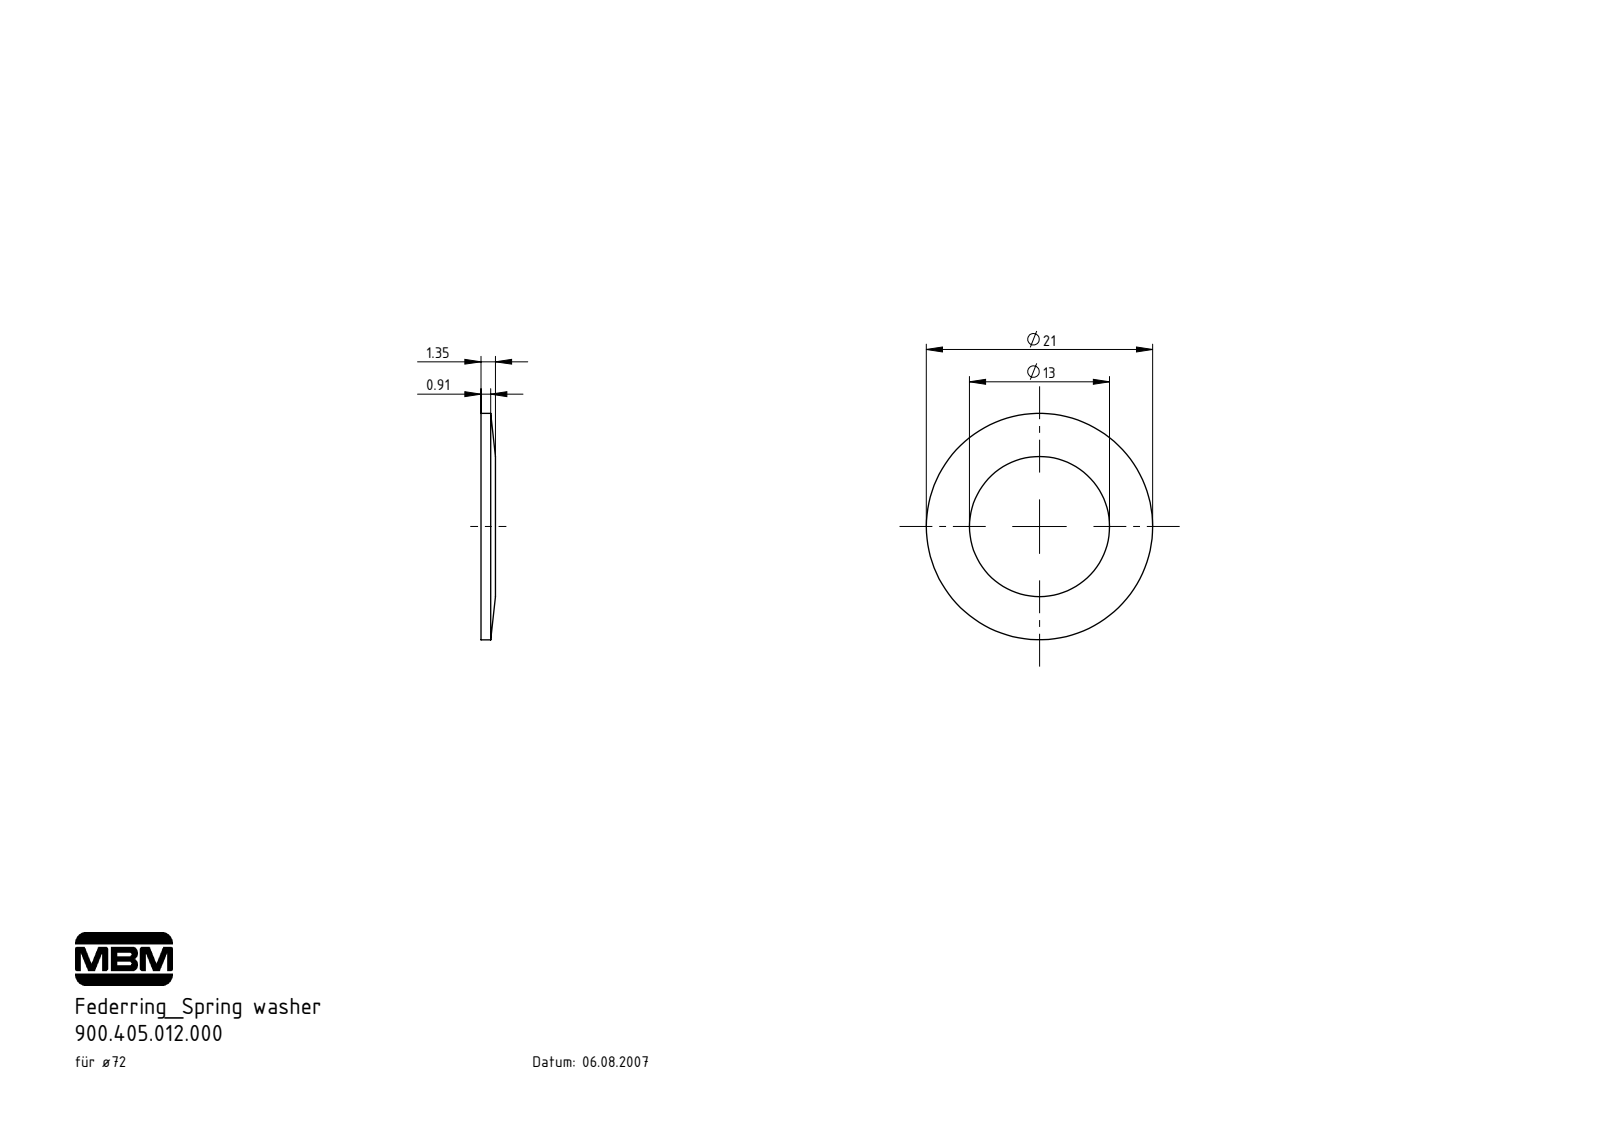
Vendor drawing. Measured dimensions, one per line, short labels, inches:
name: 900.405.012.000
written by: SolidWorks 2022 (AUTOMOTIVE_DESIGN)
unit: in
bodies: 1 solid, 6 faces (2 planar, 4 cylindrical, 0 other)
size: 0.827 × 0.827 × 0.035
volume: 0.012 in³; area: 0.811 in²
holes: 1× ⌀0.512
bosses: 1× ⌀0.827
face distances: 0.035
